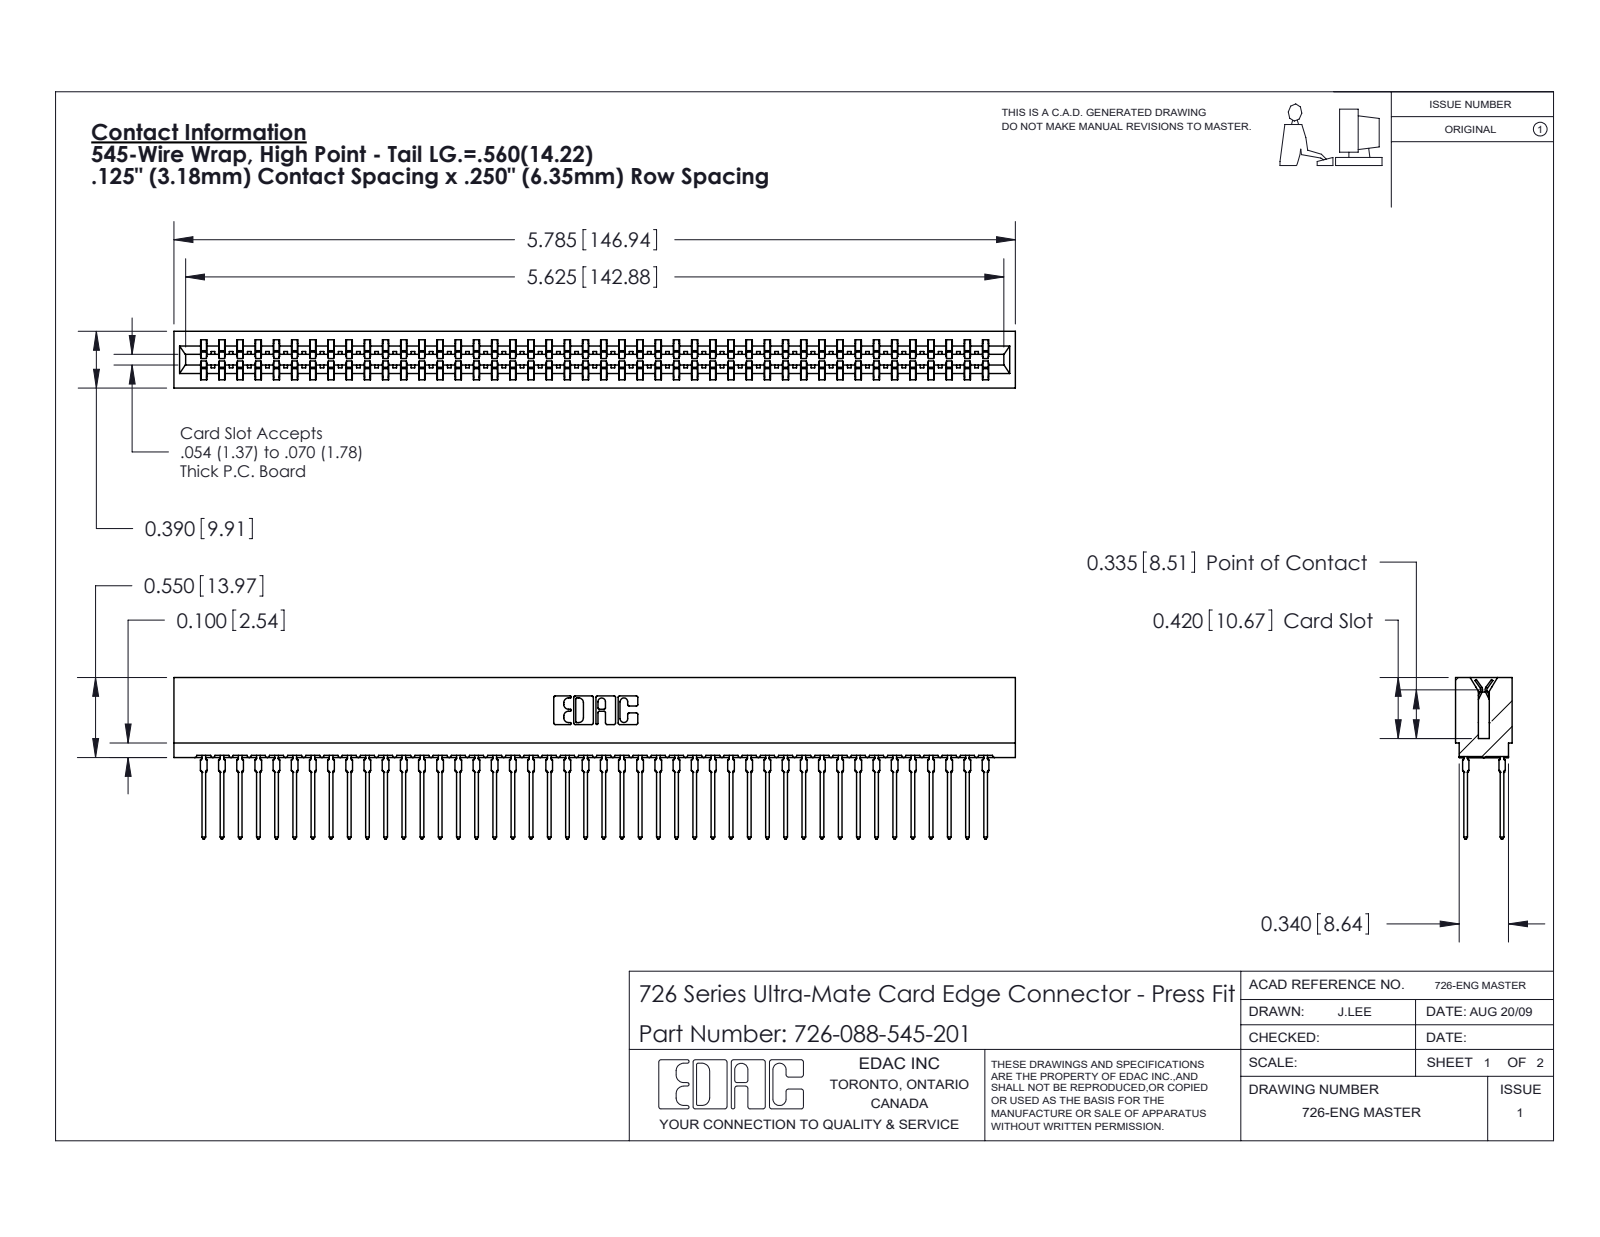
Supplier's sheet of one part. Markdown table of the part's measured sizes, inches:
| quantity | value |
| --- | --- |
| part name | 726 Part_.515 Slot Depth - 01; 746-292-001_545; 726-088-545-201 |
| STEP written by | SolidWorks 2020 (CONFIG_CONTROL_DESIGN) |
| units | inches |
| bodies | 89 solids, 7973 faces (4103 planar, 1582 cylindrical, 2288 other) |
| overall size | 5.785 × 1.109 × 0.39 |
| volume | 0.843 in³ |
| surface area | 37.92 in² |
| partial cylindrical surfaces (radius × count) | 0.021 × 176, 0.015 × 45, 0.01 × 22, 0.005 × 8, 0.011 × 8, 0.007 × 6, 0.031 × 6, 0.026 × 3 |
| main face-to-face distances | 0.057, 0.333, 0.025, 0.307, 0.25, 0.39, 0.083, 0.275, 0.365, 0.032 |
